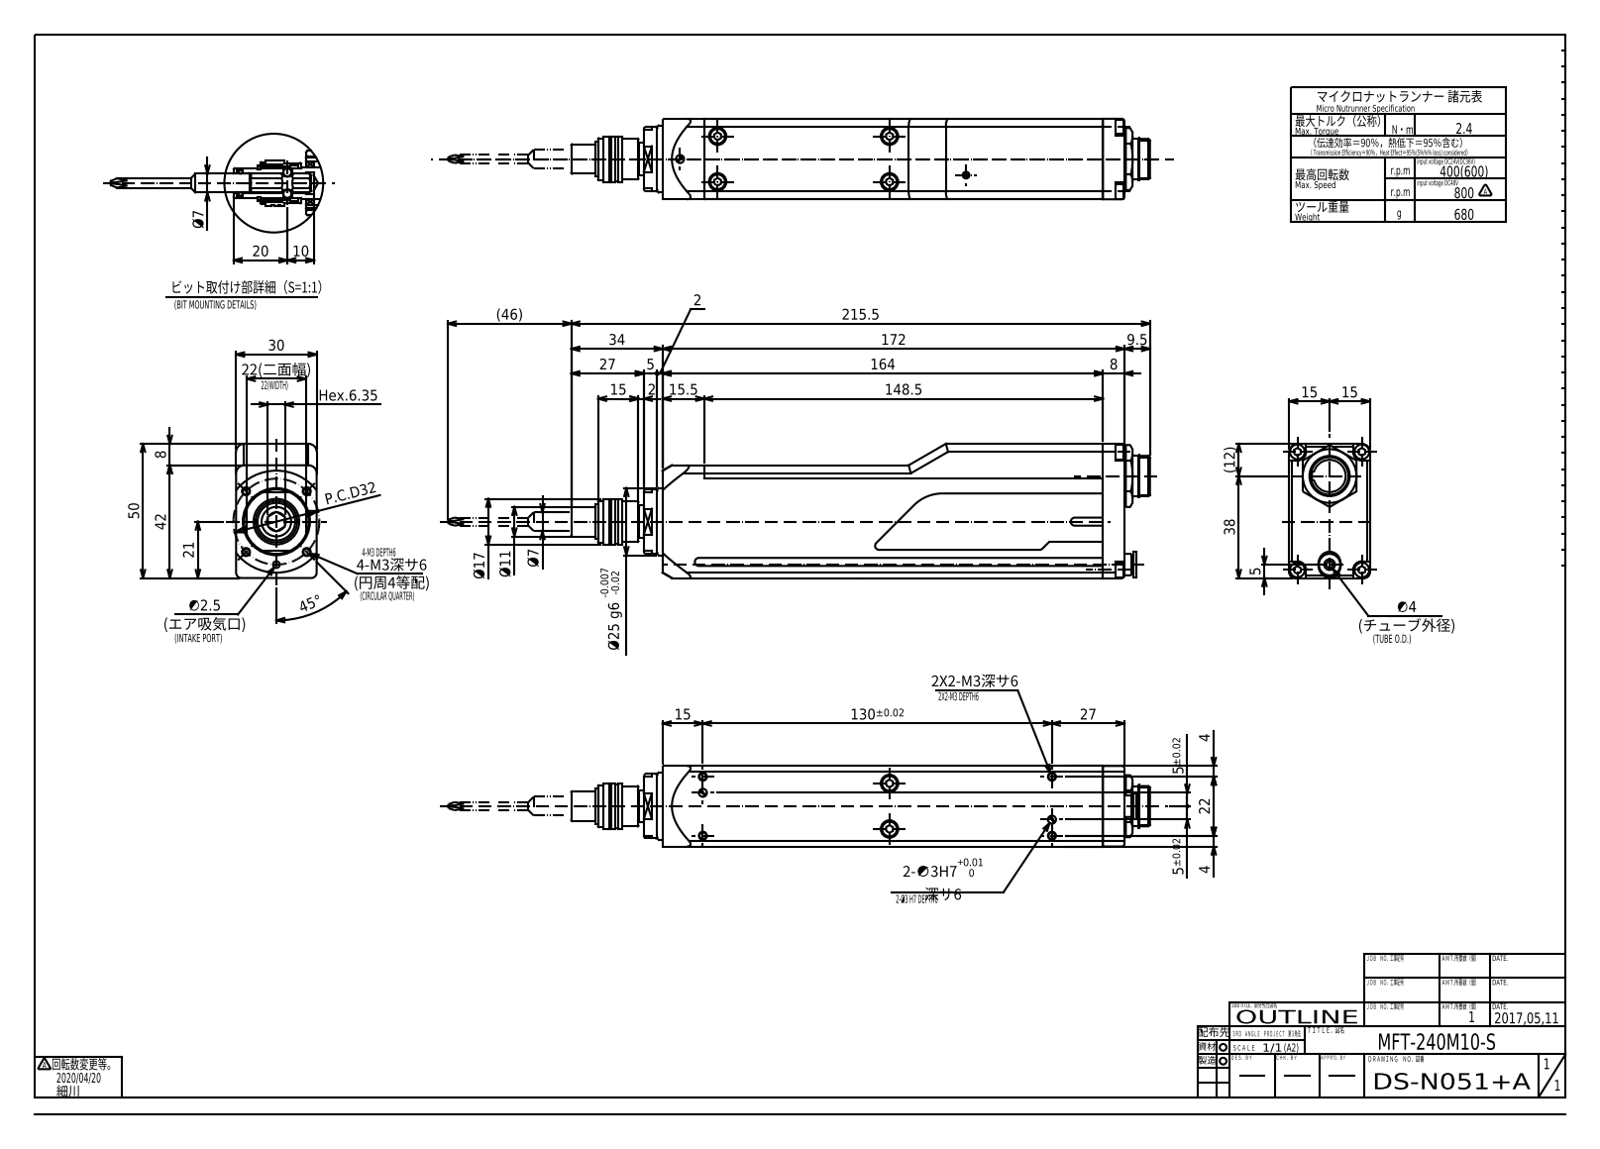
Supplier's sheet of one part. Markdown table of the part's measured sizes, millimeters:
| quantity | value |
| --- | --- |
| part name | MFT-240M10-S |
| STEP written by | SolidWorks 2017 (CONFIG_CONTROL_DESIGN) |
| units | millimeters |
| bodies | 5 solids, 398 faces (204 planar, 141 cylindrical, 53 other) |
| overall size | 215.5 × 50 × 30 |
| volume | 237 484 mm³ |
| surface area | 45 411 mm² |
| round holes (diameter × count) | 1.6 × 5, 2.9 × 4, 6 × 4, 3 × 2, 6.5 × 2, 2.5 × 1, 3.5 × 1, 5 × 1, 7 × 1, 12 × 1 |
| round bosses / shafts (diameter × count) | 5.5 × 10, 15 × 2, 25 × 1, 24 × 1, 20 × 1, 17 × 1, 16 × 1, 15.5 × 1 |
| partial cylindrical surfaces (radius × count) | 3 × 9, 1.5 × 4, 7 × 1, 11.54 × 1, 15 × 1 |
| main face-to-face distances | 30, 0.5, 29.5, 37, 37.01, 8, 5, 29, 42, 4.99 |
| hole center spacings | 15.99, 17, 22.62, 16, 6, 6.04, 9, 12.24 |
